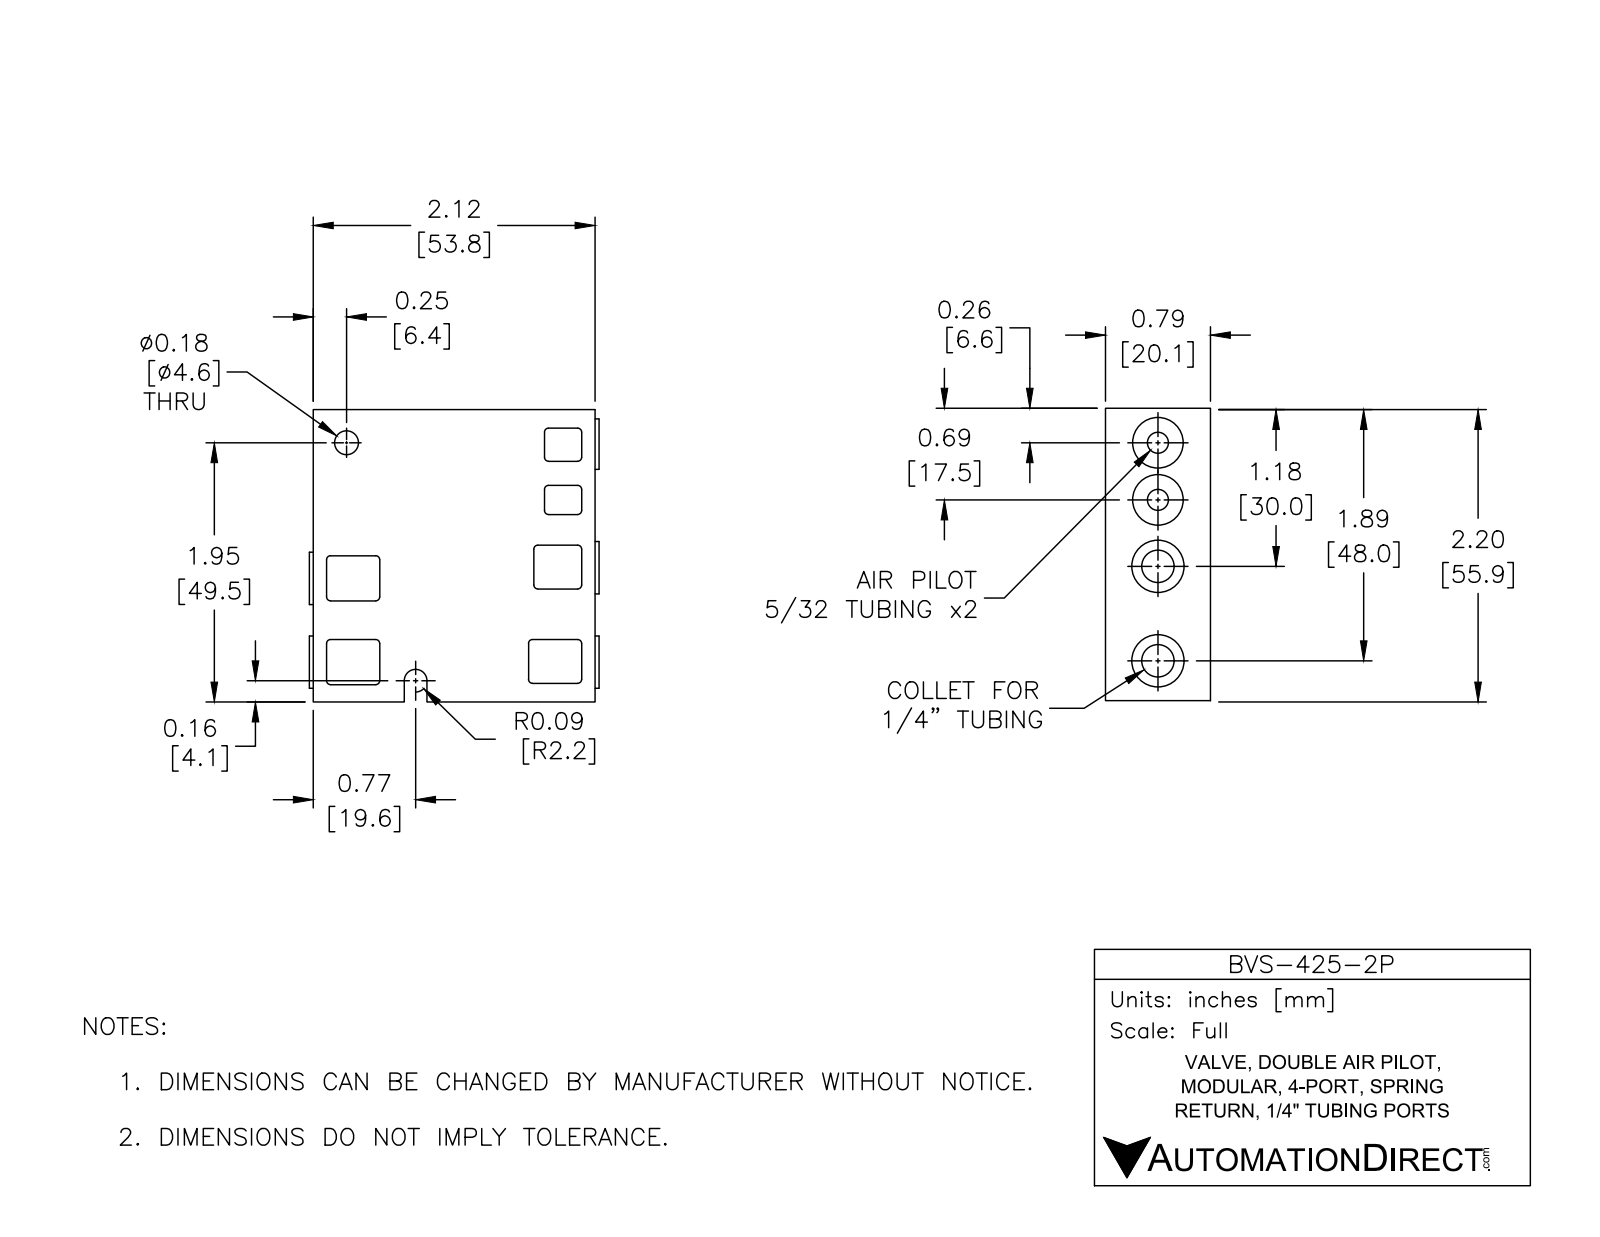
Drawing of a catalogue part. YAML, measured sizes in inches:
part_name: "BVS-425-2P"
step_written_by: "SolidWorks 2016 (AUTOMOTIVE_DESIGN)"
units: inches
bodies: {solids: 1, faces: 159, planar: 82, cylindrical: 77, other: 0}
overall_size: [2.2, 2.18, 0.79]
volume: 3.251
surface_area: 22.45
round_holes:
  - {diameter: 0.254, count: 3}
  - {diameter: 0.32, count: 2}
  - {diameter: 0.06, count: 1}
  - {diameter: 0.18, count: 1}
round_bosses_or_shafts:
  - {diameter: 0.394, count: 3}
  - {diameter: 0.38, count: 2}
partial_cylinders:
  - {radius: 0.03, count: 24}
  - {radius: 0.085, count: 1}
face_to_face_distances: [0.79, 0.1, 2.2, 0.69, 2.12, 0.59, 0.13, 0.03, 2.15, 0.78]
hole_center_spacings: [0.08, 0.43, 0.5, 0.58, 0.63, 0.71, 0.93, 1.01]
